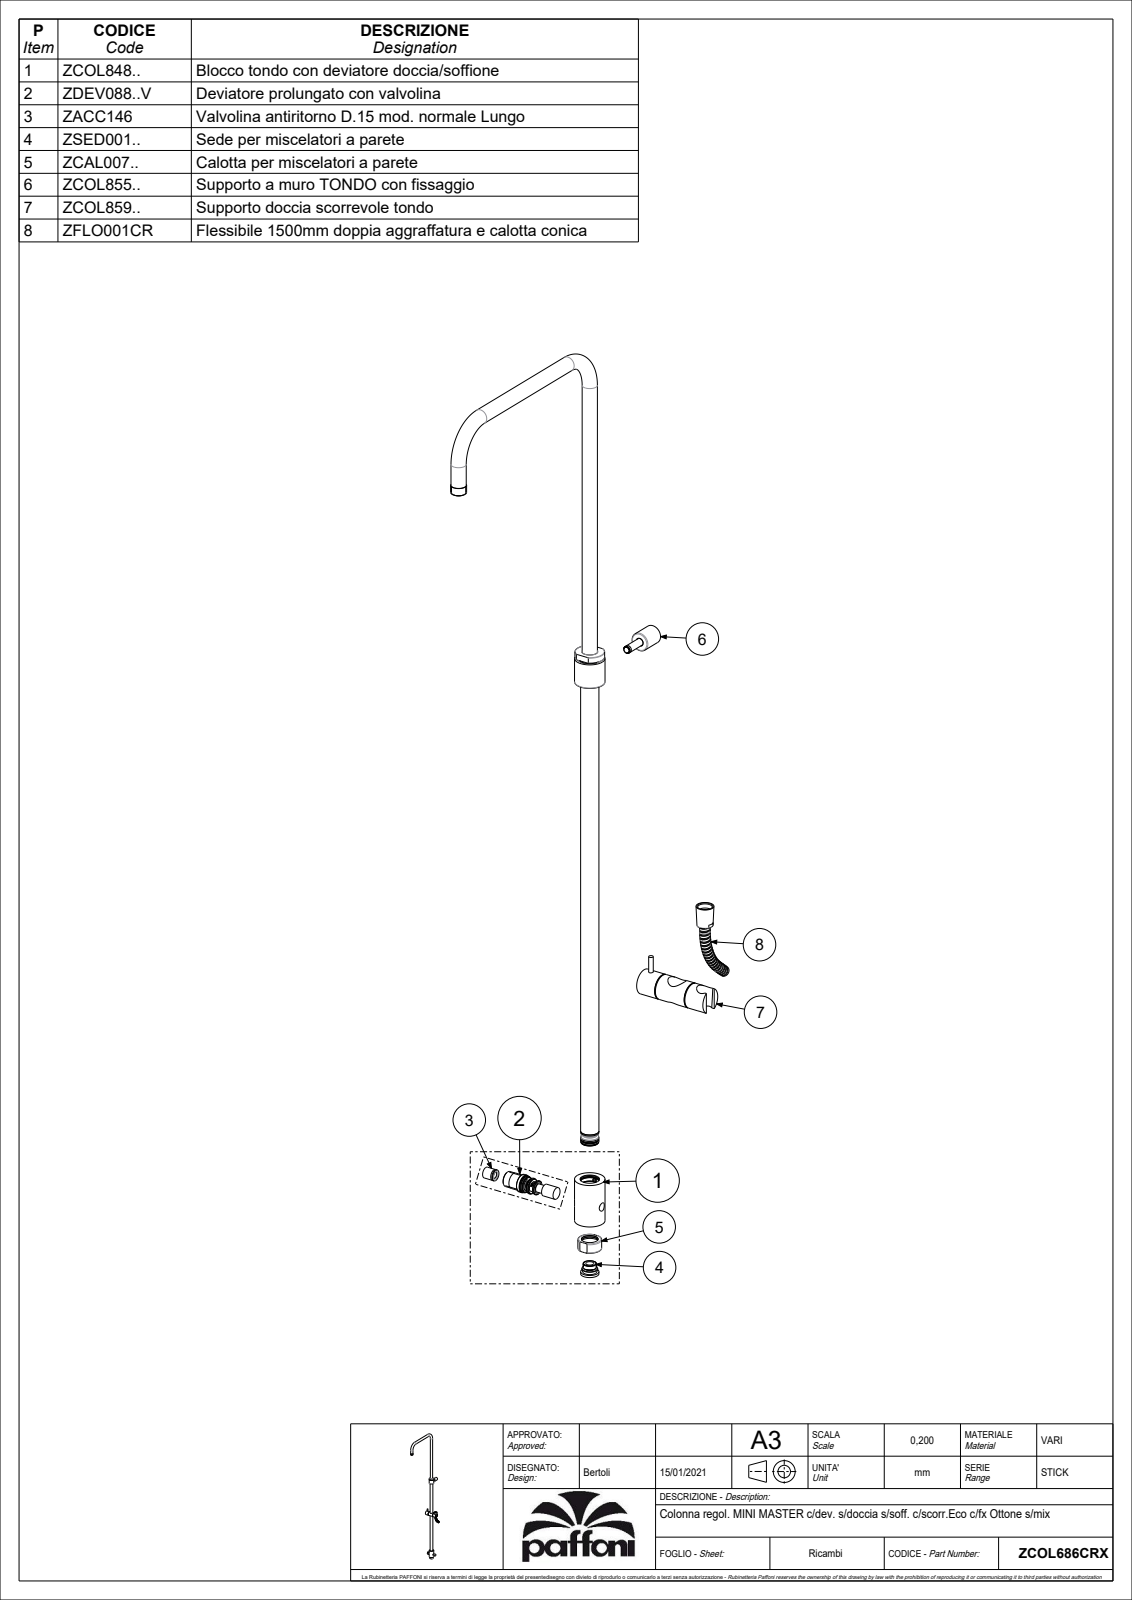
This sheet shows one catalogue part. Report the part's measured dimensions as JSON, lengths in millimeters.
{"part_name": "ZCOL686CRX", "step_written_by": "CREO PARAMETRIC BY PTC INC, 2020044 (CONFIG_CONTROL_DESIGN)", "units": "millimeters", "bodies": {"solids": 5, "faces": 686, "planar": 231, "cylindrical": 216, "other": 239}, "overall_size": [1215, 384.5, 109.25], "volume_mm3": 370075, "surface_area_mm2": 278419, "round_holes": [[5, 5], [17, 3], [10, 2], [10.5, 2], [25, 2], [3.3, 1], [3.5, 1], [4.2, 1], [4.5, 1], [6.2, 1], [8.5, 1], [10.2, 1]], "round_bosses_or_shafts": [[20, 3], [24, 2], [21, 2], [20.5, 2], [40, 1], [34, 1], [33.5, 1], [28, 1]], "partial_cylinders_radius": [[9.75, 1], [15.6, 1], [19.5, 1]], "face_to_face_distances": [8, 10, 60, 754, 694, 44.5, 709.5, 649.5, 744, 746], "hole_center_spacings": [4.85, 7.89, 8, 9.55, 12.46, 37.91, 39.45, 47.42]}
